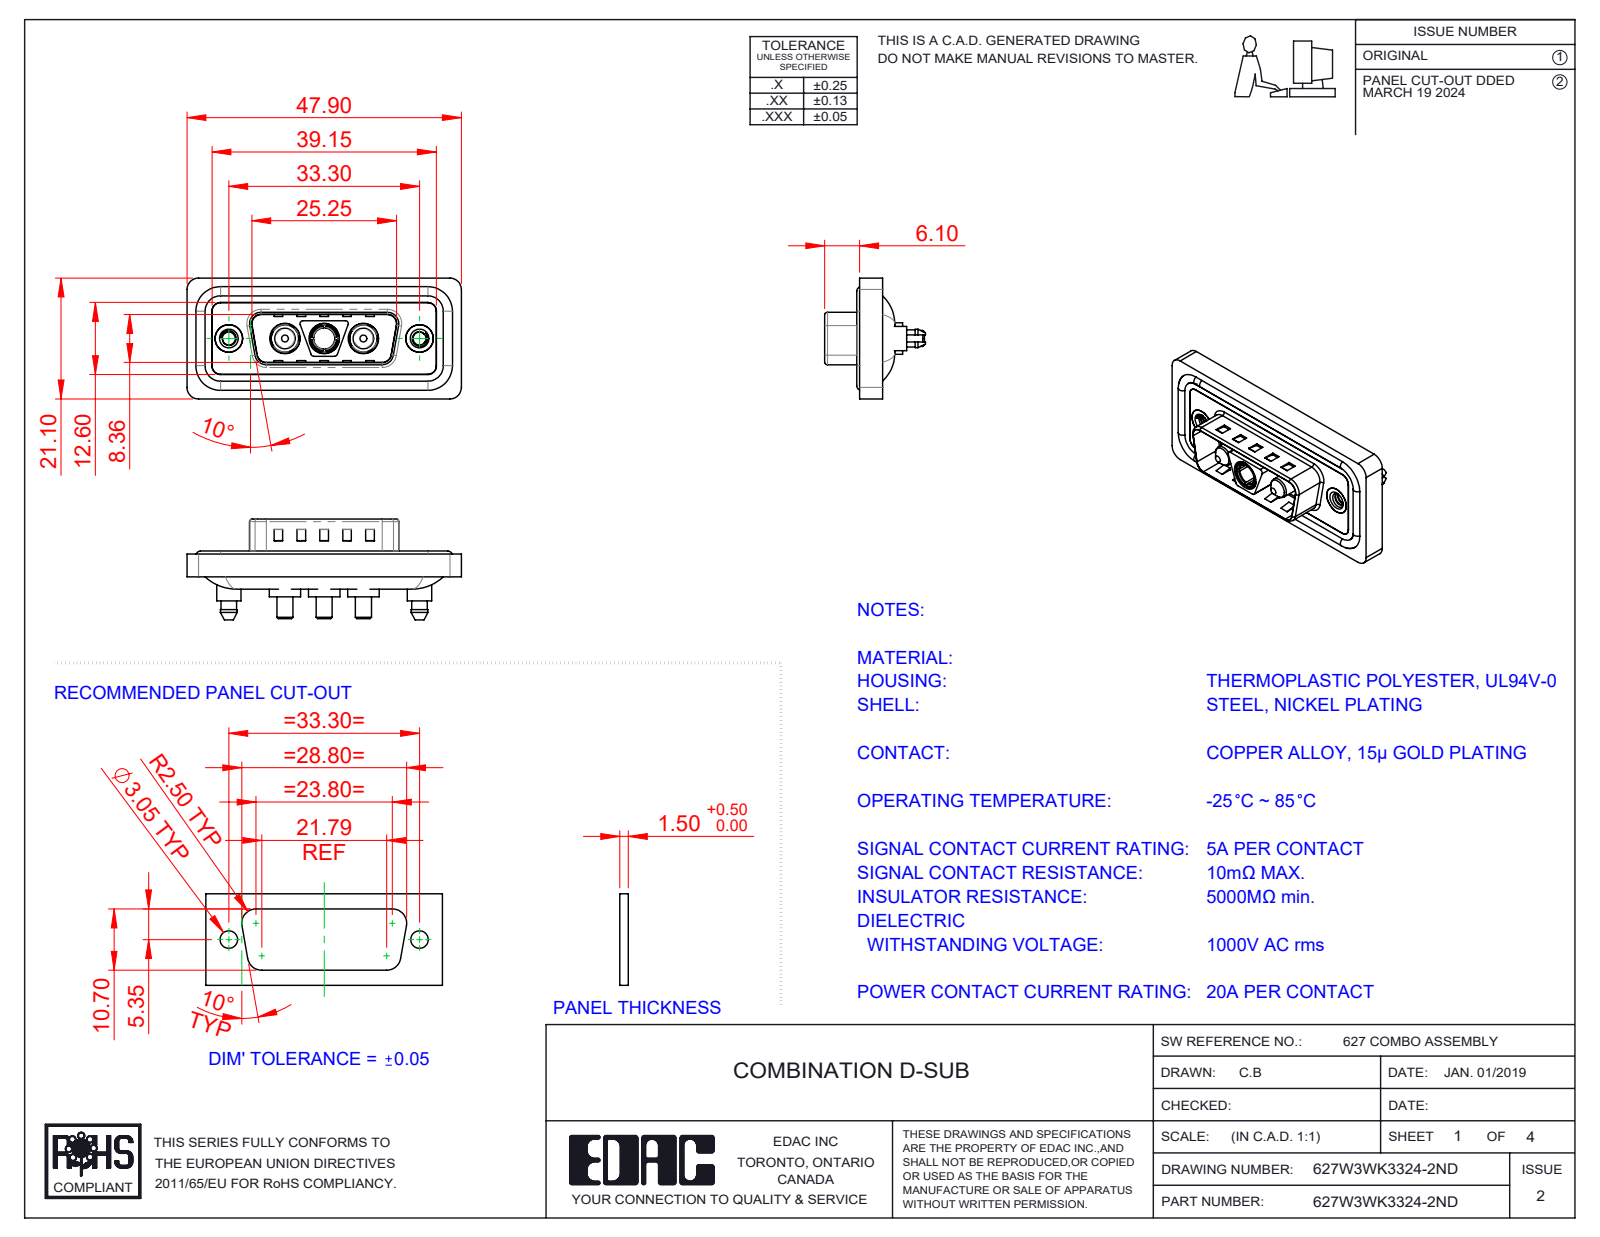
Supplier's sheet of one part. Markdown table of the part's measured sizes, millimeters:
| quantity | value |
| --- | --- |
| part name | 627Combo Threaded Boardlock_5; Power Pin_20A S; 627Combo Waterproof Housing_15 Contacts; 627Combo Housing_3WK3 (+5 more) |
| STEP written by | SolidWorks 2023 (CONFIG_CONTROL_DESIGN) |
| units | millimeters |
| bodies | 13 solids, 667 faces (247 planar, 290 cylindrical, 130 other) |
| overall size | 47.9 × 21.1 × 17.6 |
| volume | 5 823 mm³ |
| surface area | 9 463 mm² |
| round holes (diameter × count) | 4.85 × 3, 5.3 × 3, 2.26 × 2, 4 × 2, 4.8 × 2, 5 × 2, 3.7 × 1 |
| round bosses / shafts (diameter × count) | 1.6 × 4, 5.5 × 3, 5.2 × 3, 4.75 × 3, 3.75 × 3, 2.8 × 3, 5.4 × 2, 4.9 × 2 |
| partial cylindrical surfaces (radius × count) | 1.5 × 28, 2 × 20, 0.5 × 12, 1.6 × 10, 0.25 × 4, 0.6 × 4, 0.65 × 4, 0.9 × 4 |
| main face-to-face distances | 0.4, 1.1, 1.5, 0.5, 1.6, 3.1, 2.9, 4, 0.7, 0.82 |
| hole center spacings | 6.85, 9.8, 16.65, 23.5, 13.7, 33.3 |
